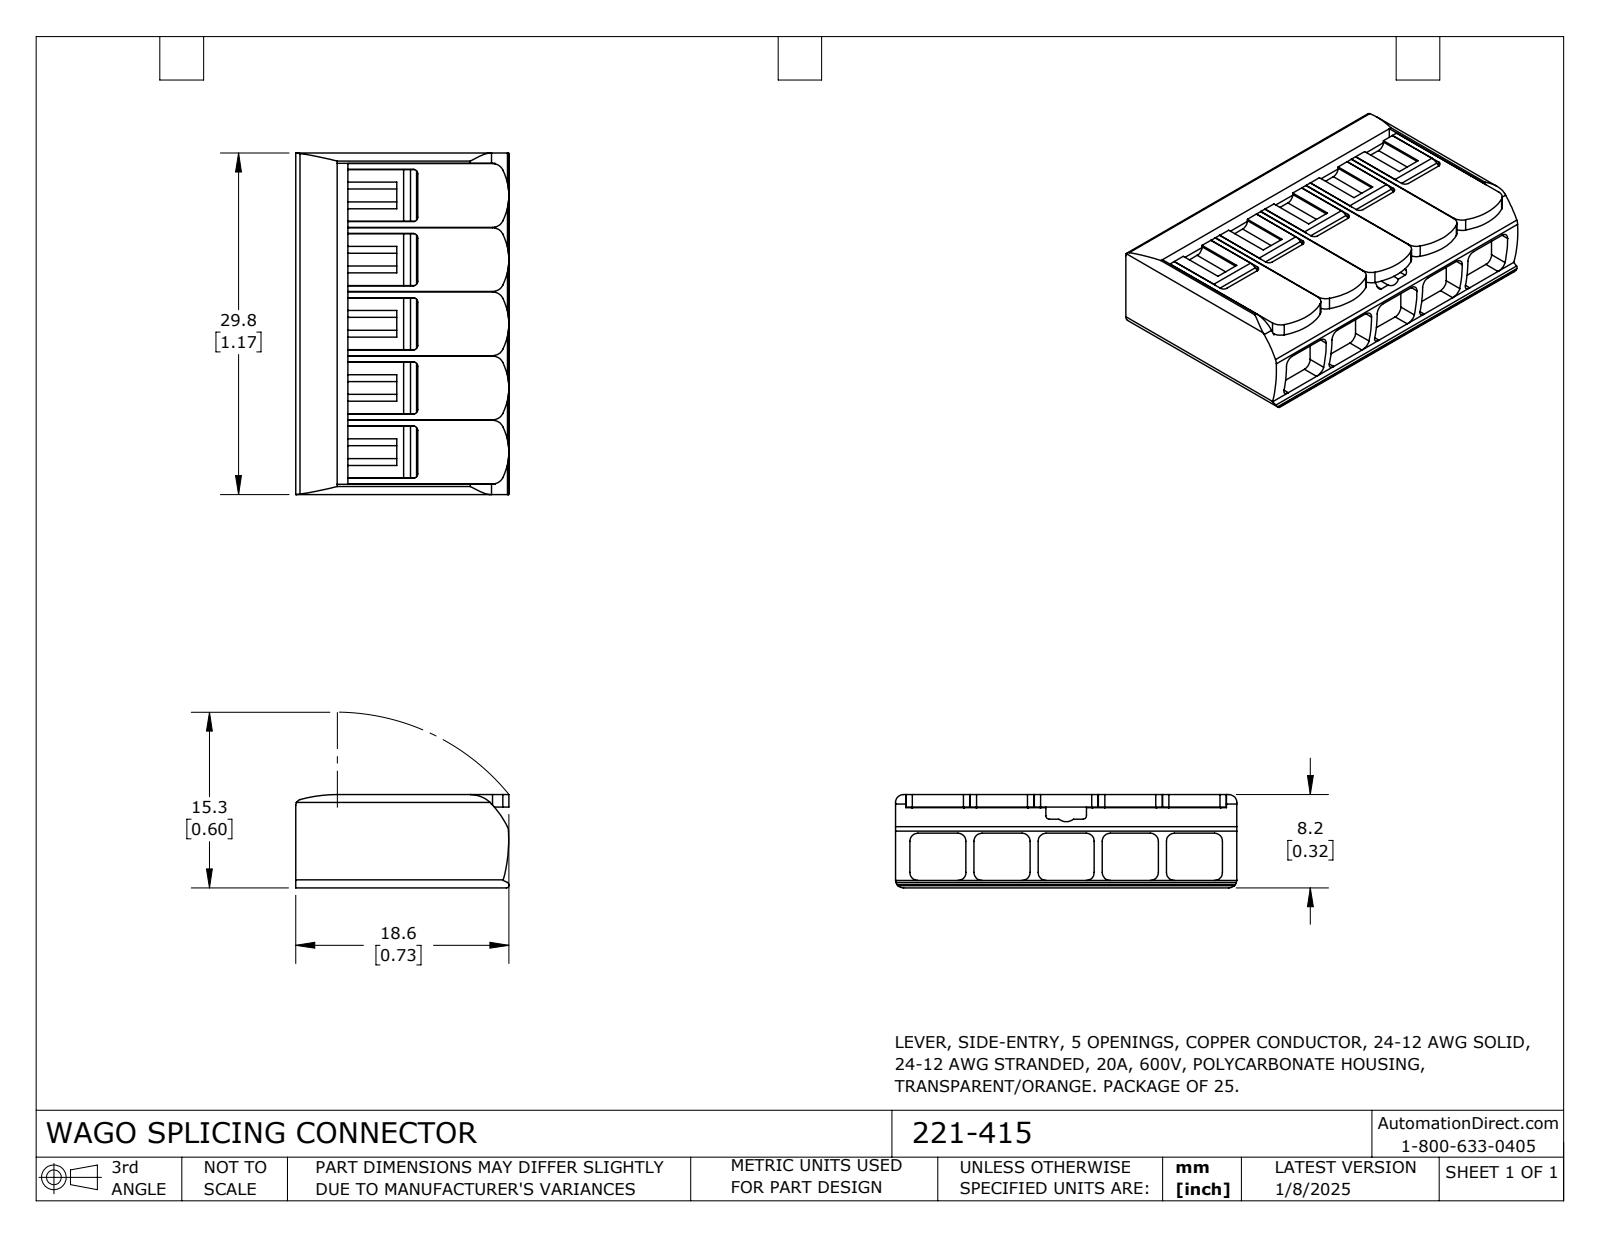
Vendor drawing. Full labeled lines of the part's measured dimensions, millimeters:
Part name (STEP PRODUCT): 221-415
STEP written by: SolidWorks 2023 (CONFIG_CONTROL_DESIGN)
Units: millimetres
Bodies: 1 solid, 235 faces (144 planar, 91 cylindrical, 0 other)
Overall size (bounding box): 29.8 × 18.6 × 8.15
Volume: 4 139 mm³ · Surface area: 2 610 mm²
Partial cylindrical surfaces — rounded edges, fillets, slot ends (radius × count): R0.7 ×24, R1 ×12, R0.4 ×10, R0.6 ×10, R0.3 ×6, R5 ×5, R0.2 ×4, R0.5 ×1
Main face-to-face distances: 8.15, 5.6, 29.8, 16.6, 11.2, 7, 1.15, 7.05, 1.1, 5.56
